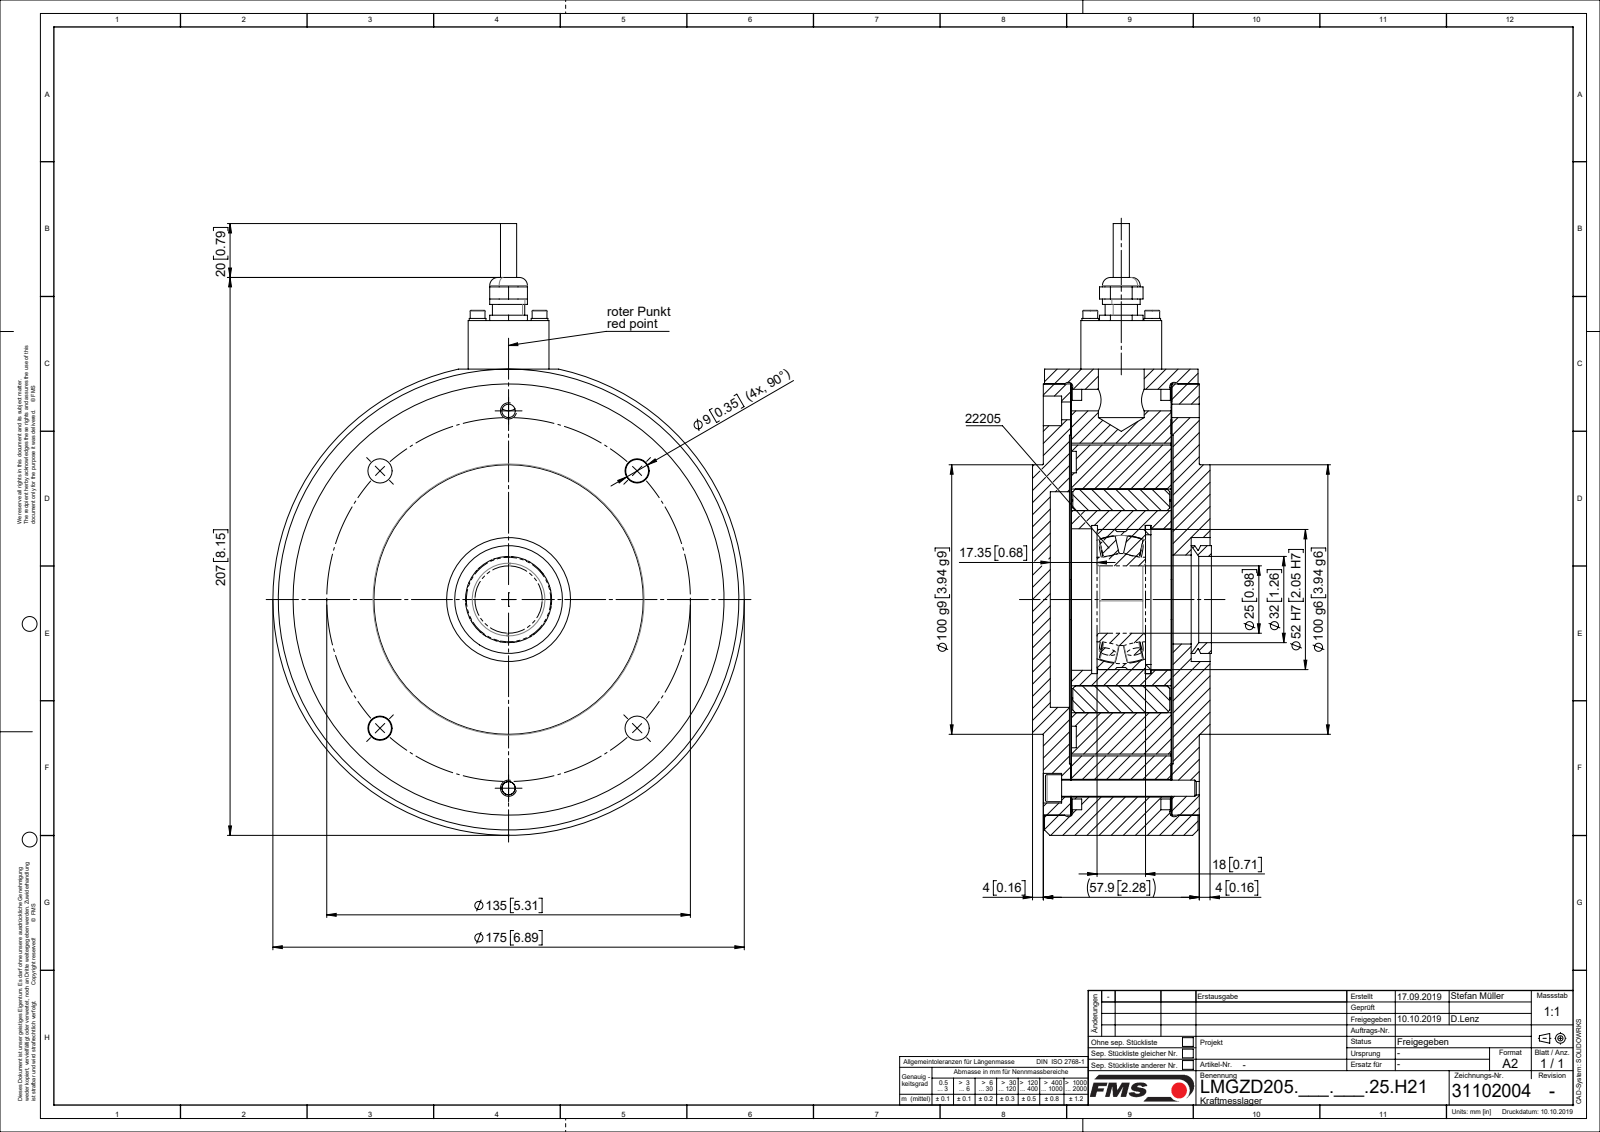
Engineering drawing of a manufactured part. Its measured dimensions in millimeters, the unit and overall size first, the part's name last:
Units: millimetres
Overall size (bounding box): 227 × 175 × 66.4
Round holes (diameter × count): ⌀2.5 ×6, ⌀3.1 ×4, ⌀3.4 ×4, ⌀9 ×4, ⌀3.2 ×3, ⌀5 ×2, ⌀6.6 ×2, ⌀8 ×2, ⌀8.5 ×2, ⌀11 ×2, ⌀6 ×1, ⌀10 ×1
Round bosses / shafts (diameter × count): ⌀6.2 ×4, ⌀5.5 ×4, ⌀3 ×4, ⌀175 ×1, ⌀160 ×1, ⌀148 ×1, ⌀100 ×1, ⌀94 ×1
Partial cylindrical surfaces — rounded edges, fillets, slot ends (radius × count): R0.1 ×4, R4.24 ×2, R7.5 ×2, R9 ×2, R11 ×2, R20.8 ×1, R24.1 ×1
Main face-to-face distances: 37.25, 10.2, 10.45, 47.45, 47.7, 37, 37.5, 0.5, 9.7, 48.2
Hole centre spacings: 16.26, 23, 48.92, 52.67, 67.5, 95.46, 97.25, 127.04
Volume: 1 291 000 mm³ · Surface area: 270 353 mm²
Bodies: 53 solids, 742 faces (208 planar, 262 cylindrical, 272 other)
Part name (STEP PRODUCT): 47663_01; 47664_01; Zyl-Schr DIN912_M6x50; 43404.01_01 (+8 more)
STEP written by: SolidWorks 2018 (CONFIG_CONTROL_DESIGN)
